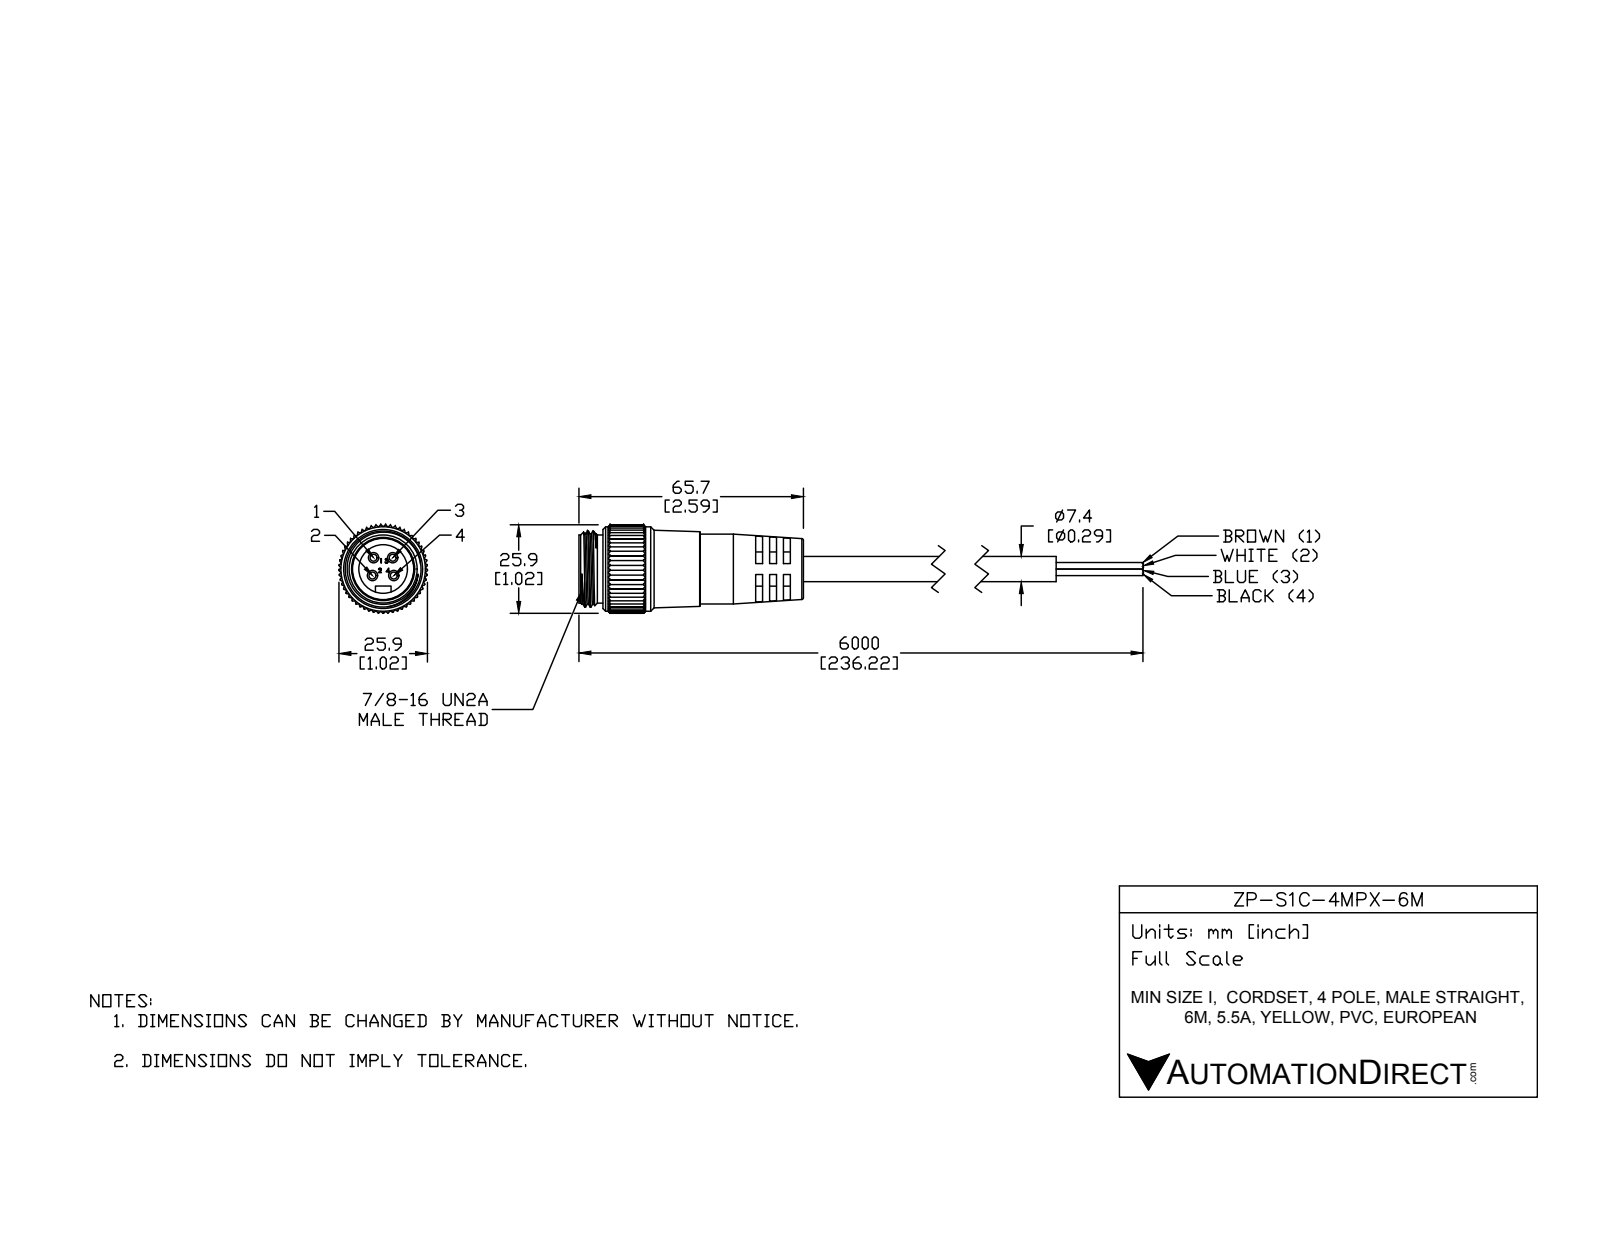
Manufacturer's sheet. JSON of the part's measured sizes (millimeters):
{"part_name": "ZP-S1C-4MPX-6M", "step_written_by": "SolidWorks 2015 (AUTOMOTIVE_DESIGN)", "units": "millimeters", "bodies": {"solids": 6, "faces": 606, "planar": 218, "cylindrical": 326, "other": 62}, "overall_size": [115.9, 25.84, 25.83], "volume_mm3": 26095, "surface_area_mm2": 13335, "round_holes": [[14.22, 1], [17.88, 1], [19.96, 1], [20.45, 1], [21, 1]], "round_bosses_or_shafts": [[3.05, 4], [2, 4], [24.68, 1], [22.22, 1], [20.4, 1], [19.5, 1], [9.91, 1]], "partial_cylinders_radius": [[0.25, 165], [2.29, 1], [5.25, 1], [12.93, 1]], "face_to_face_distances": [2, 4.04, 13.88, 11.88, 2.04, 9.84, 6.04, 7.84, 2.02, 8.06]}
